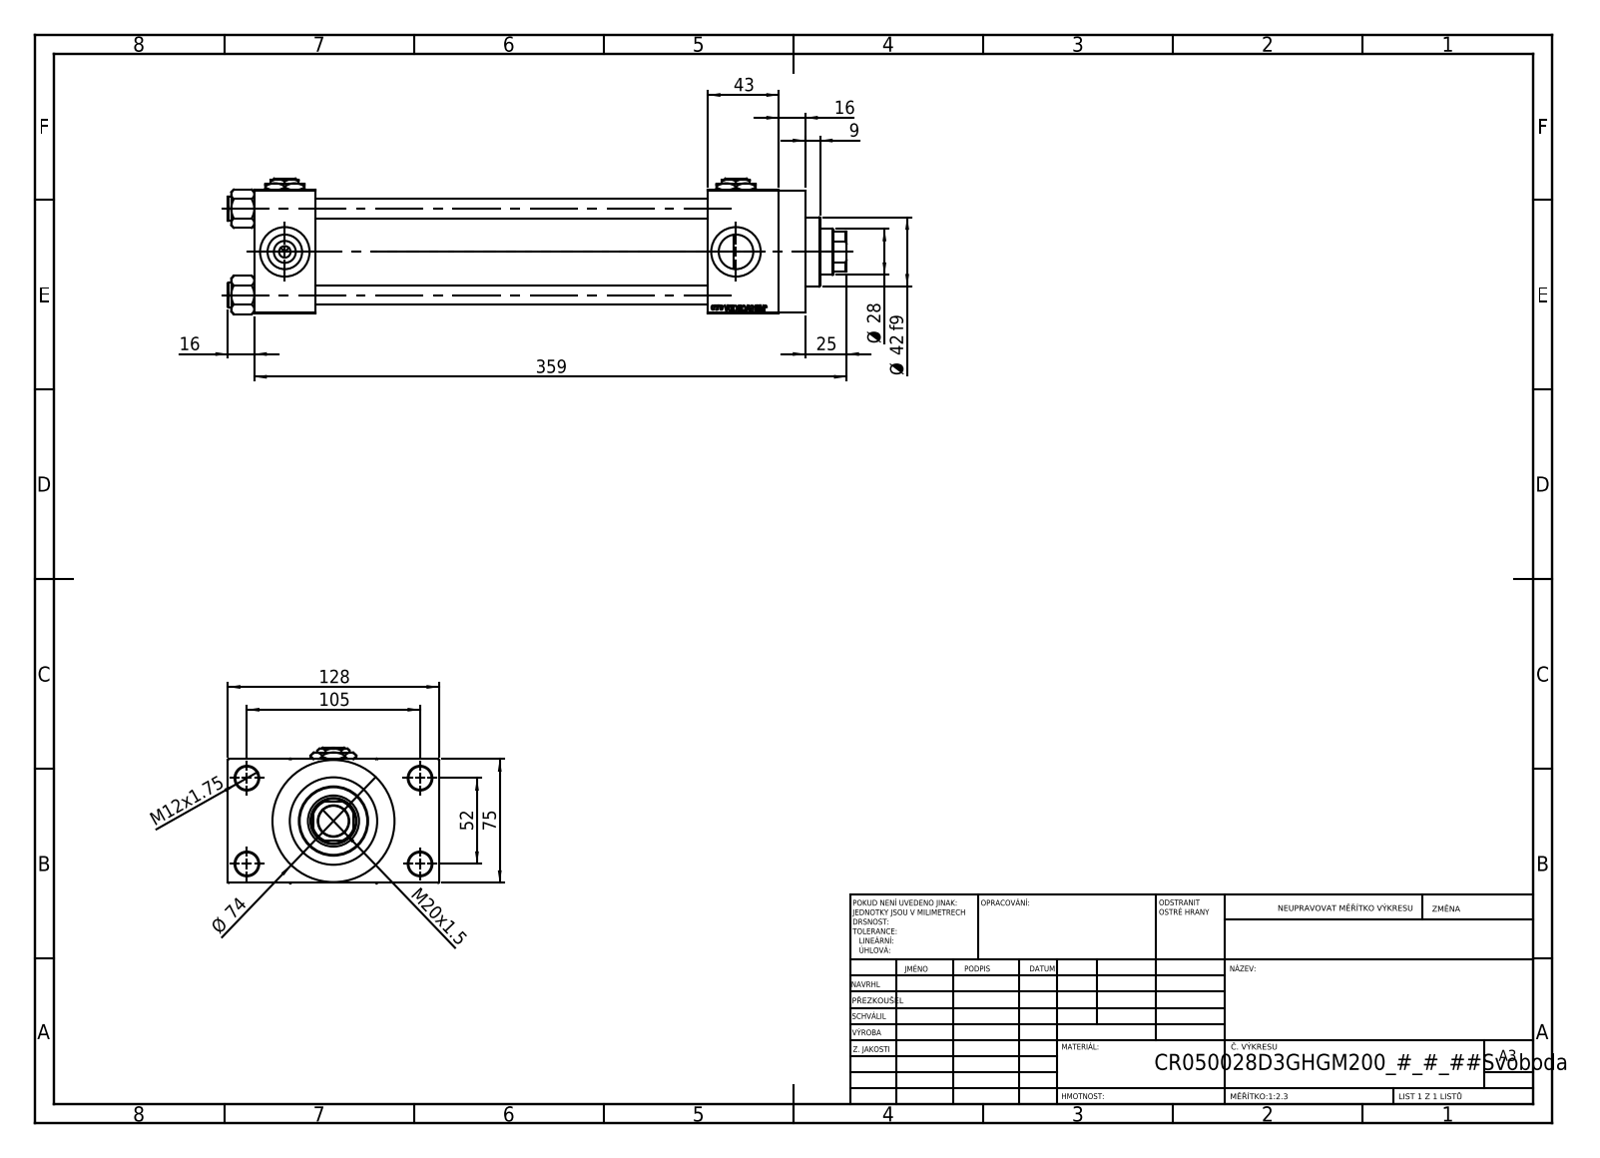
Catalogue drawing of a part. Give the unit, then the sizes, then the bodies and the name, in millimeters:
Units: millimetres
Overall size (bounding box): 375 × 128 × 82.27
Round holes (diameter × count): ⌀12 ×4, ⌀14 ×4, ⌀20.96 ×4, ⌀30 ×4, ⌀7 ×3, ⌀18.5 ×1, ⌀28 ×1, ⌀31 ×1, ⌀41 ×1, ⌀50 ×1, ⌀53 ×1
Round bosses / shafts (diameter × count): ⌀15 ×4, ⌀74 ×1, ⌀56 ×1, ⌀42 ×1
Partial cylindrical surfaces — rounded edges, fillets, slot ends (radius × count): R13.5 ×1
Main face-to-face distances: 75, 238, 37, 275, 26.5, 318, 281, 43, 101.5, 16
Hole centre spacings: 26.35, 36.98, 52.3, 58.43, 58.59, 78.65, 94.37, 52
Volume: 1 084 000 mm³ · Surface area: 277 761 mm²
Bodies: 13 solids, 1204 faces (545 planar, 99 cylindrical, 560 other)
Part name (STEP PRODUCT): NUT_M5_D; V215CR_VCP_D; V215_VC_A; V215CR_D_Body (+2 more)
STEP written by: SolidWorks 2019 (CONFIG_CONTROL_DESIGN)
